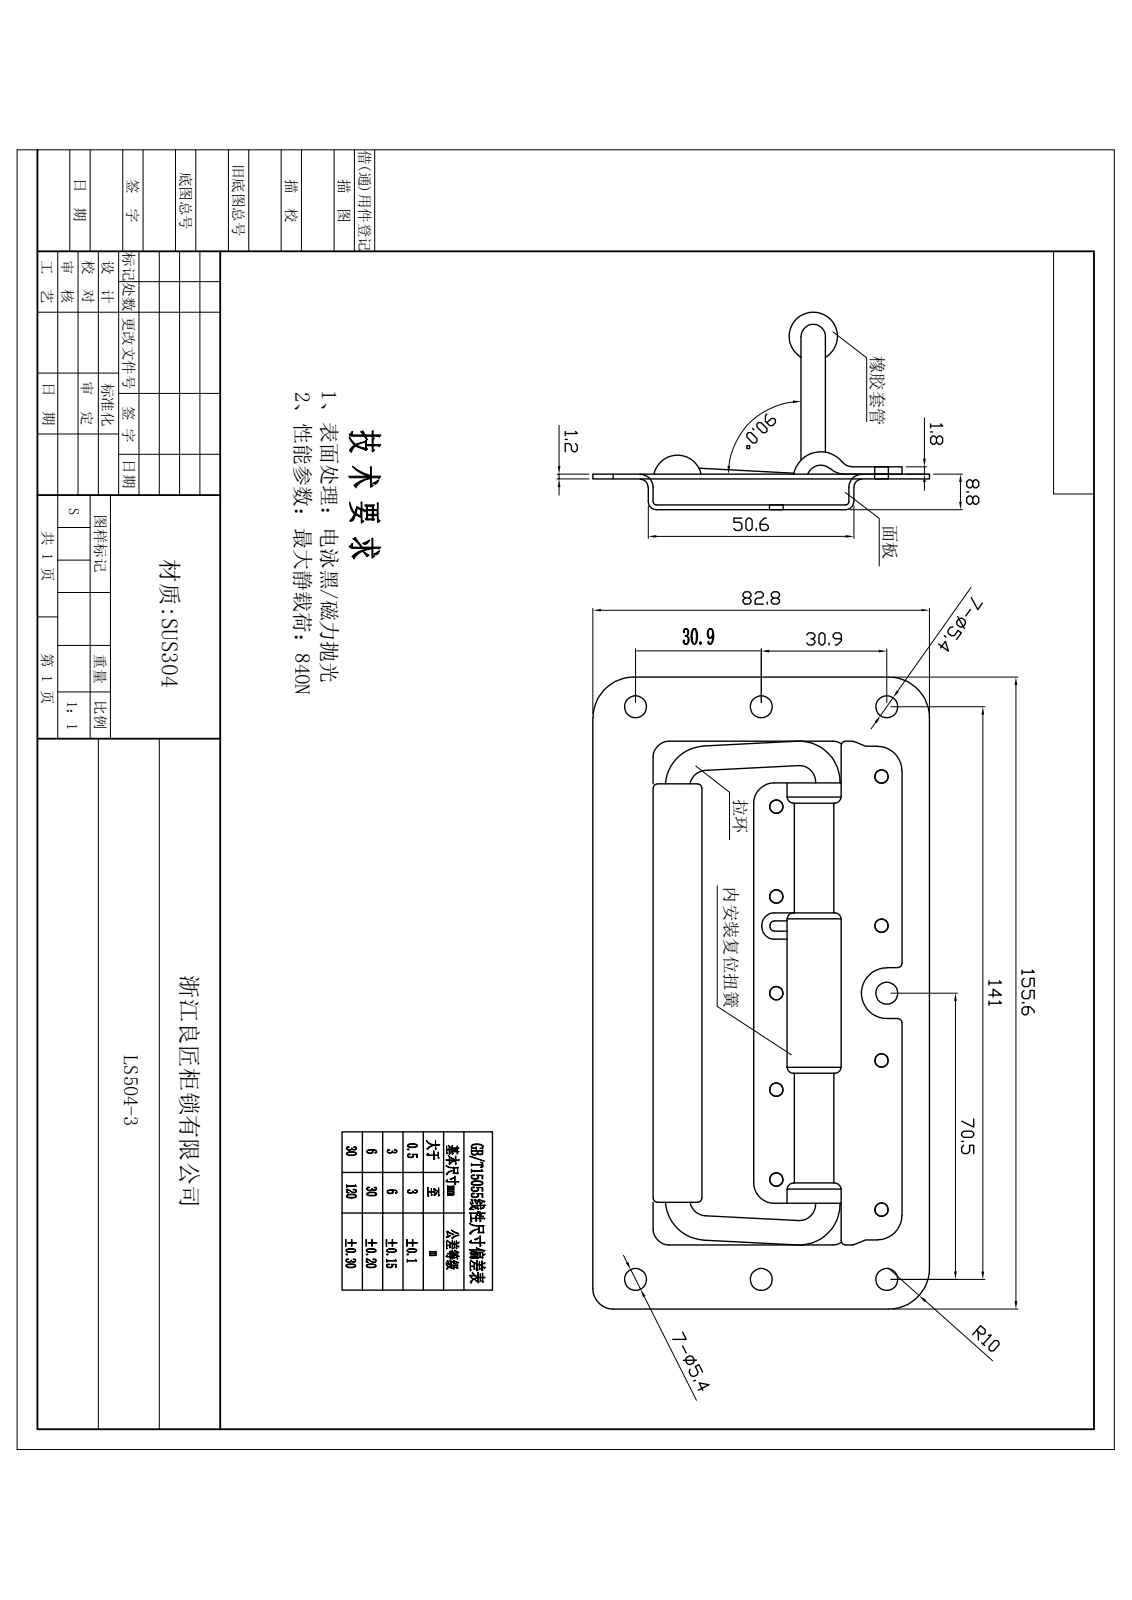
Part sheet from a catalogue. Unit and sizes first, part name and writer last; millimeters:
Units: millimetres
Overall size (bounding box): 155.58 × 82.8 × 15.5
Round holes (diameter × count): ⌀2 ×9, ⌀3.2 ×9, ⌀5.1 ×6, ⌀5.3 ×1, ⌀7 ×1
Round bosses / shafts (diameter × count): ⌀5.5 ×9, ⌀3 ×9, ⌀6 ×4, ⌀12 ×1, ⌀1.2 ×1
Partial cylindrical surfaces — rounded edges, fillets, slot ends (radius × count): R3 ×16, R5 ×8, R2 ×7, R1 ×5, R2.23 ×4, R3.18 ×4, R3.43 ×4, R3.8 ×4
Main face-to-face distances: 1.2, 7.64, 8.84, 6.44, 2, 10.84, 9.64, 3.2, 7.7, 5.7
Hole centre spacings: 22.2, 30.91, 144.39, 23.8, 23.9, 26.68, 26.7, 27.67
Volume: 41 729 mm³ · Surface area: 52 605 mm²
Bodies: 14 solids, 456 faces (80 planar, 216 cylindrical, 160 other)
Part name (STEP PRODUCT): 700-22422-01_BAR_WK_HDL_1; 700-22422-01_RUBBER_TUBE_HDL_1; 700-22422-01_RIVET_HDL_1; 700-22422-01_MOUNT_BASE_HDL_1 (+3 more)
STEP written by: Rhino 8.5 (CONFIG_CONTROL_DESIGN)
